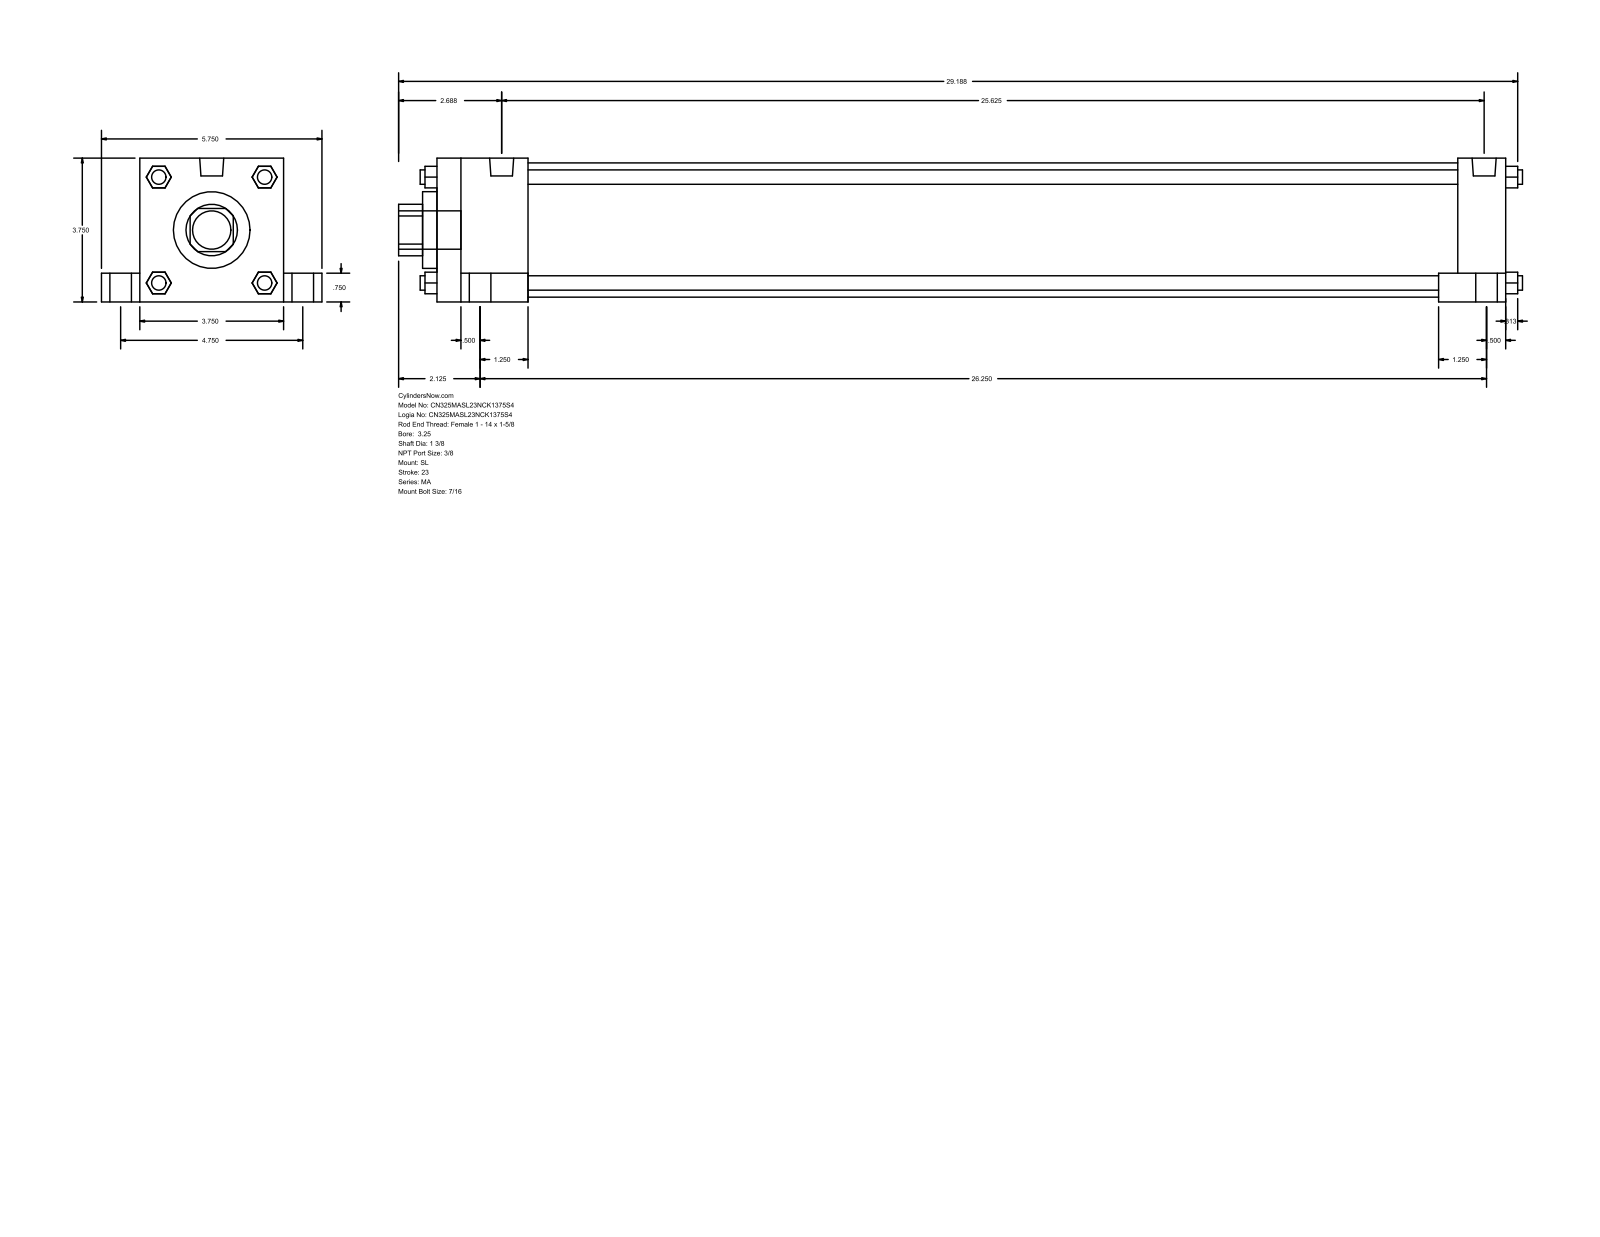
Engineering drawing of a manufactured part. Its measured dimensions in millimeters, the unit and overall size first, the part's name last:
Units: millimetres
Overall size (bounding box): 744.54 × 146.05 × 95.25
Round holes (diameter × count): ⌀34.92 ×1, ⌀50.8 ×1, ⌀88.9 ×1
Round bosses / shafts (diameter × count): ⌀20.64 ×4, ⌀14.29 ×4, ⌀11.11 ×4, ⌀9.53 ×4, ⌀15.93 ×2, ⌀25.4 ×1
Partial cylindrical surfaces — rounded edges, fillets, slot ends (radius × count): R17.06 ×1
Main face-to-face distances: 95.24, 708.02, 615.95, 25.41, 120.65, 676.27, 31.75, 60.32, 647.7, 19.05
Bodies: 0 solids, 148 faces (112 planar, 36 cylindrical, 0 other)
Part name (STEP PRODUCT): MA_SL__0325_1.375
STEP written by: GSSL Pune (CONFIG_CONTROL_DESIGN)
